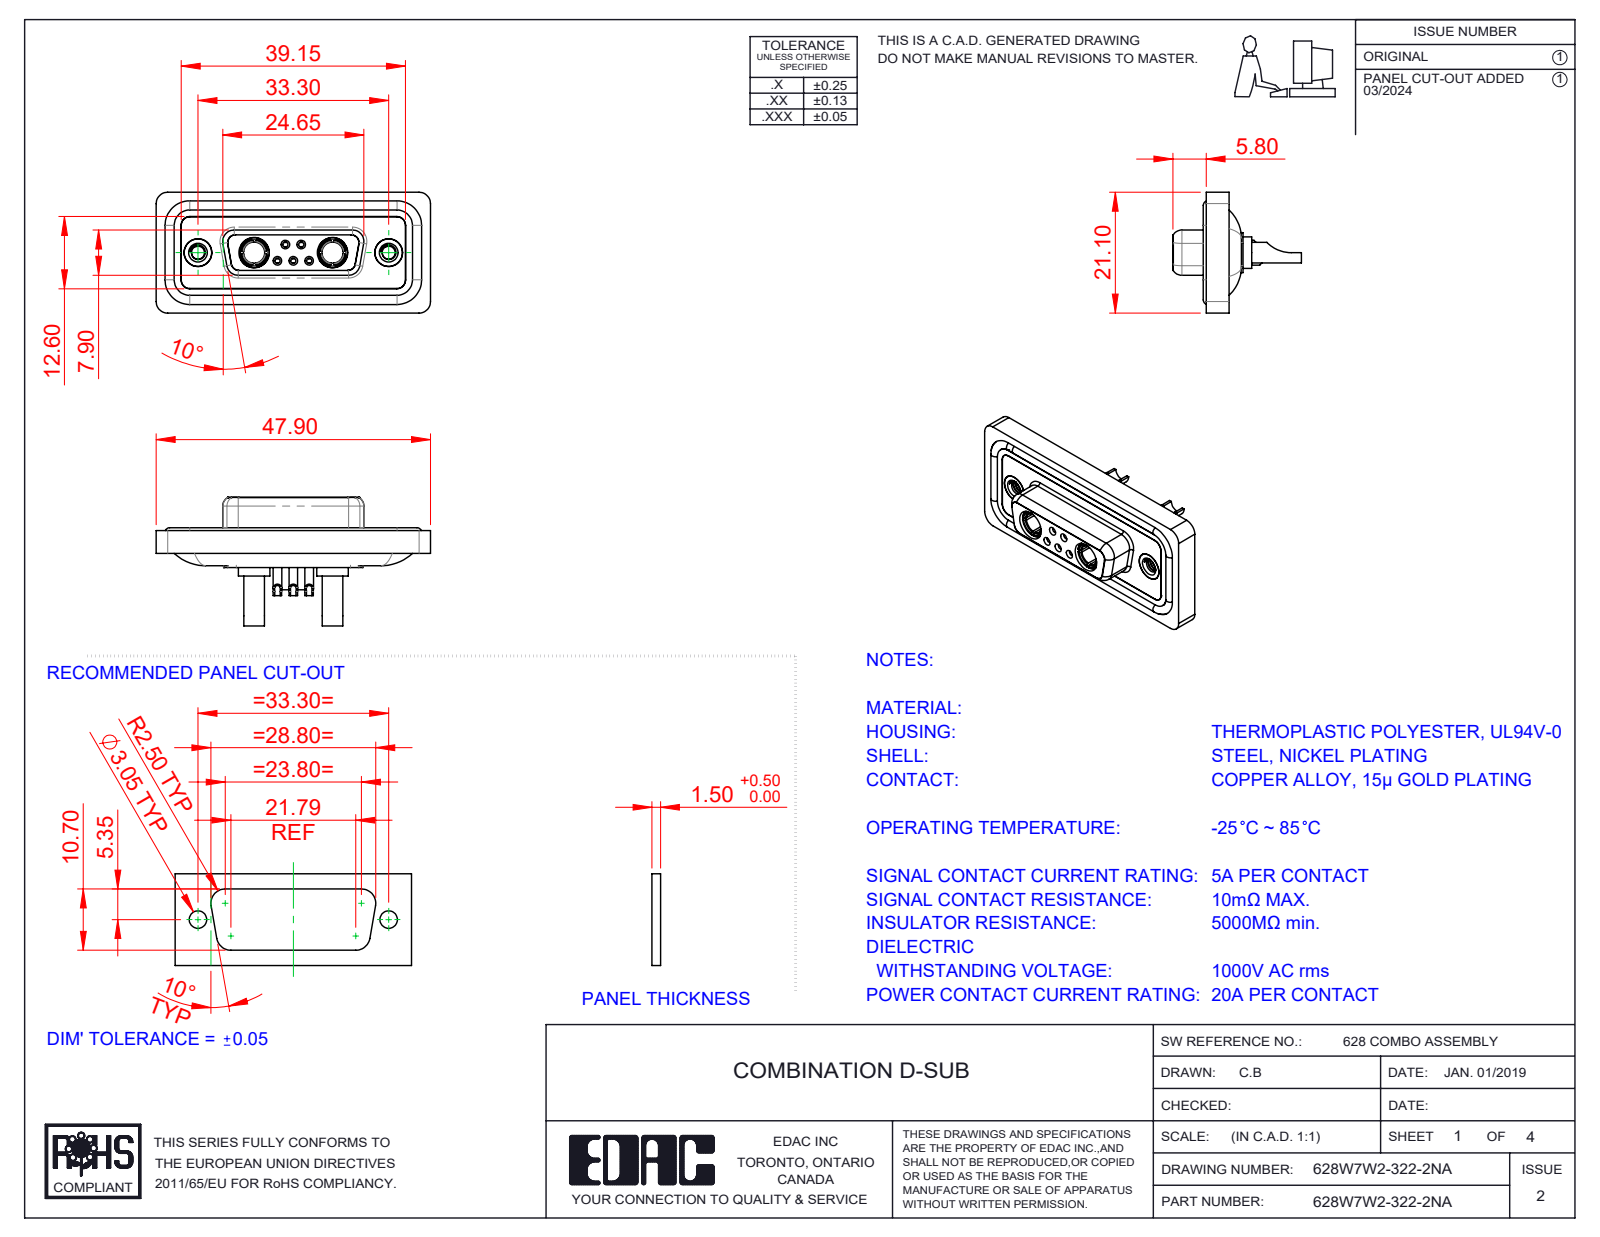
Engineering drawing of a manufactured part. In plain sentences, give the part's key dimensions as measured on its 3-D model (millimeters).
The part is named "Power Socket_20A SC; 628Combo Shell Rear_15 Contacts; 628W7W2-322-2NA; 628Combo Shell Front_15 Contacts (+5 more)". Its 3-D file was written by "SolidWorks 2023 (CONFIG_CONTROL_DESIGN)". It is 16 solids with 819 faces: 254 planar, 347 cylindrical and 218 other. Overall it measures 47.9 by 22.45 by 21.1 millimeters. Its volume is 6 115 cubic millimeters and its surface area 10 102 square millimeters. Round holes: 5 of diameter 0.9, 5 of diameter 1, 5 of diameter 1.1, 5 of diameter 1.5, 5 of diameter 2, 4 of diameter 4.85, 3 of diameter 1.6, 2 of diameter 1.7, 2 of diameter 2.26, 2 of diameter 2.7, 2 of diameter 3.7, 2 of diameter 4. Round bosses or shafts: 6 of diameter 1.6, 5 of diameter 2.2, 2 of diameter 5.5, 2 of diameter 5.2, 2 of diameter 4.96, 2 of diameter 4.95, 2 of diameter 4.8, 2 of diameter 4.75. Partial cylindrical surfaces (rounded edges, fillets, slot ends): 22 of radius 1.5, 20 of radius 2, 12 of radius 1.35, 8 of radius 1.6, 6 of radius 1, 4 of radius 0.25, 4 of radius 0.5, 4 of radius 0.6. The main face-to-face distances are 0.4, 1.8, 1.6, 0.5, 2.9, 1.1, 7.45, 5.65, 6.6, 7.05. The hole center spacings are 3.16, 2.77, 9.8, 23.5, 4.31, 4.33, 5.03, 5.04.
